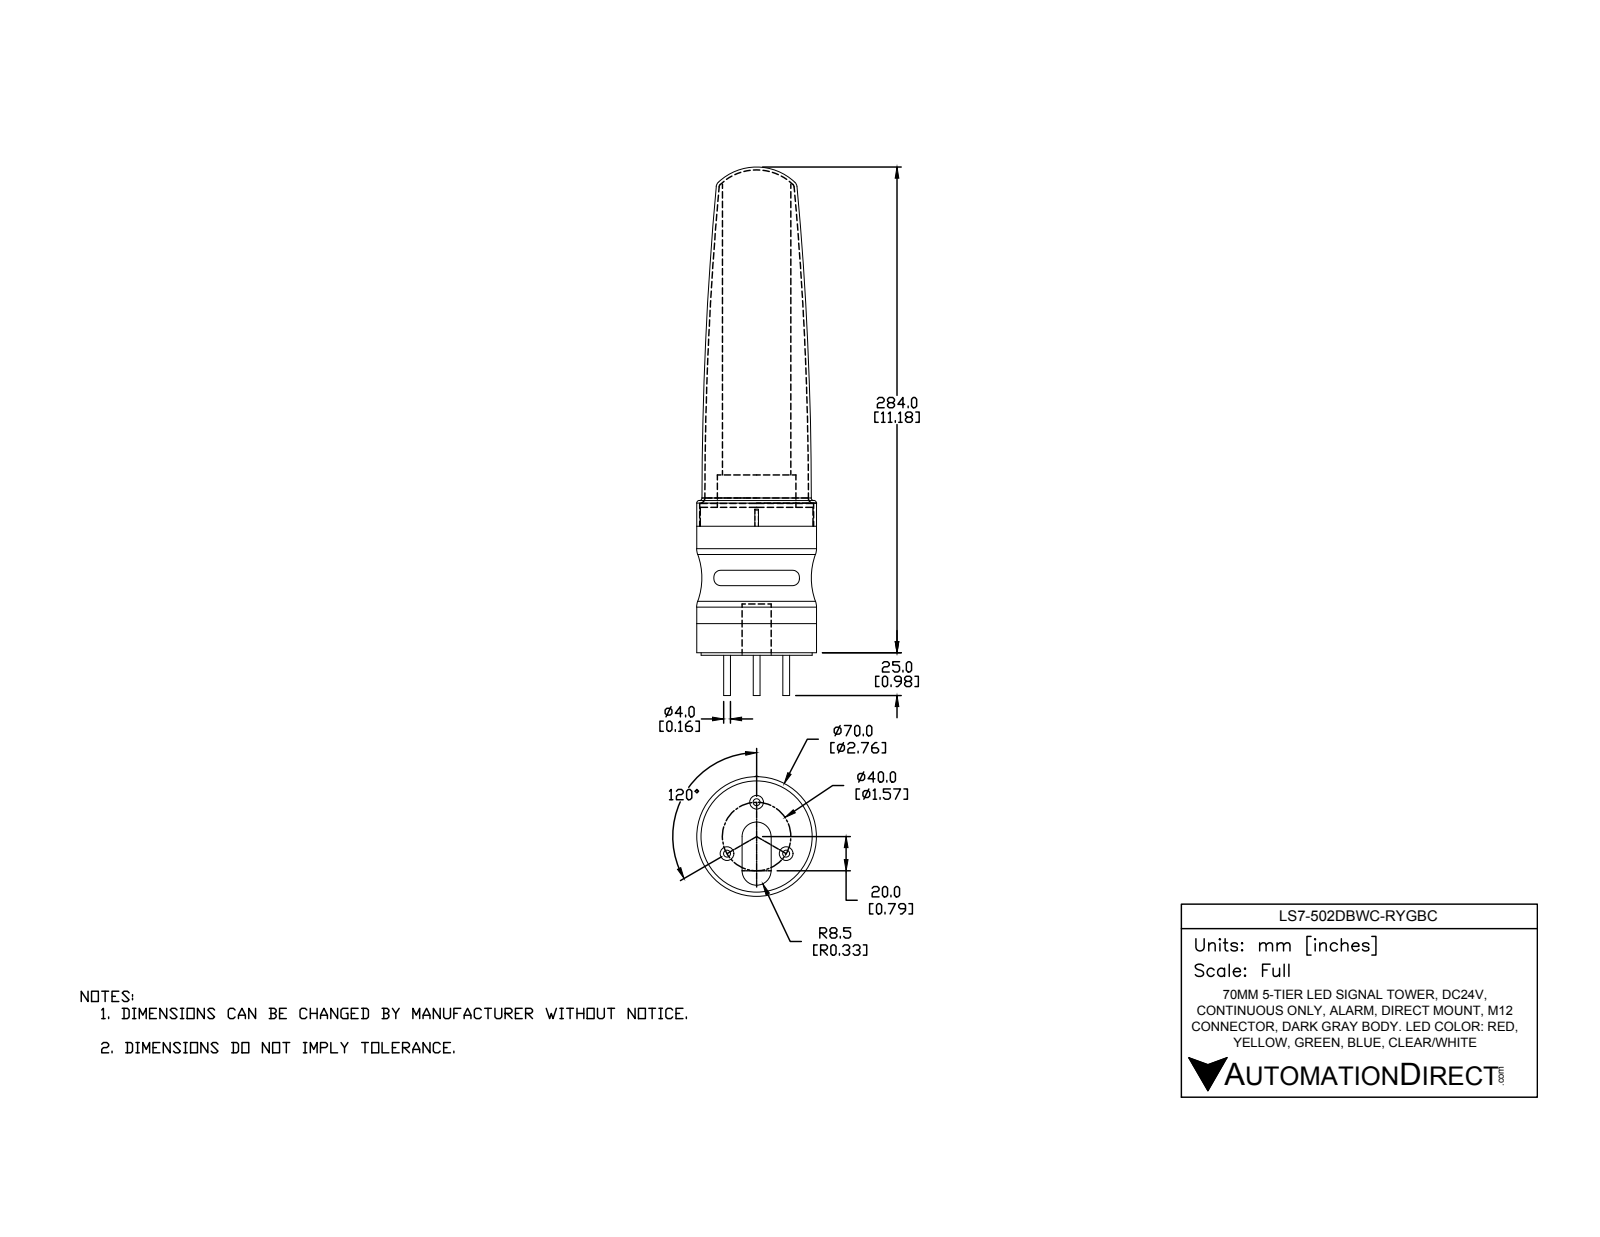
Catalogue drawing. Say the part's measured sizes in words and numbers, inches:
The part is named "LS7-502DBWC-RYGBC". Its 3-D file was written by "SolidWorks 2016 (AUTOMOTIVE_DESIGN)". It is 8 solids with 101 faces: 32 planar, 45 cylindrical and 24 other. Overall it measures 12.165 by 2.768 by 2.756 inches. Its volume is 36.36 cubic inches and its surface area 230.6 square inches. Round holes: 3 of diameter 0.315, 1 of diameter 2.622. Round bosses or shafts: 3 of diameter 0.157, 1 of diameter 2.756, 1 of diameter 2.598, 1 of diameter 2.559, 1 of diameter 1.811, 1 of diameter 1.575. Partial cylindrical surfaces (rounded edges, fillets, slot ends): 4 of radius 0.157, 2 of radius 0.335, 1 of radius 0.039, 1 of radius 0.079. The main face-to-face distances are 0.669, 4.094, 3.425, 0.059, 0.728, 4.154, 3.406, 3.346, 2.677, 0.748. The hole center spacings are 0.787, 1.364.
